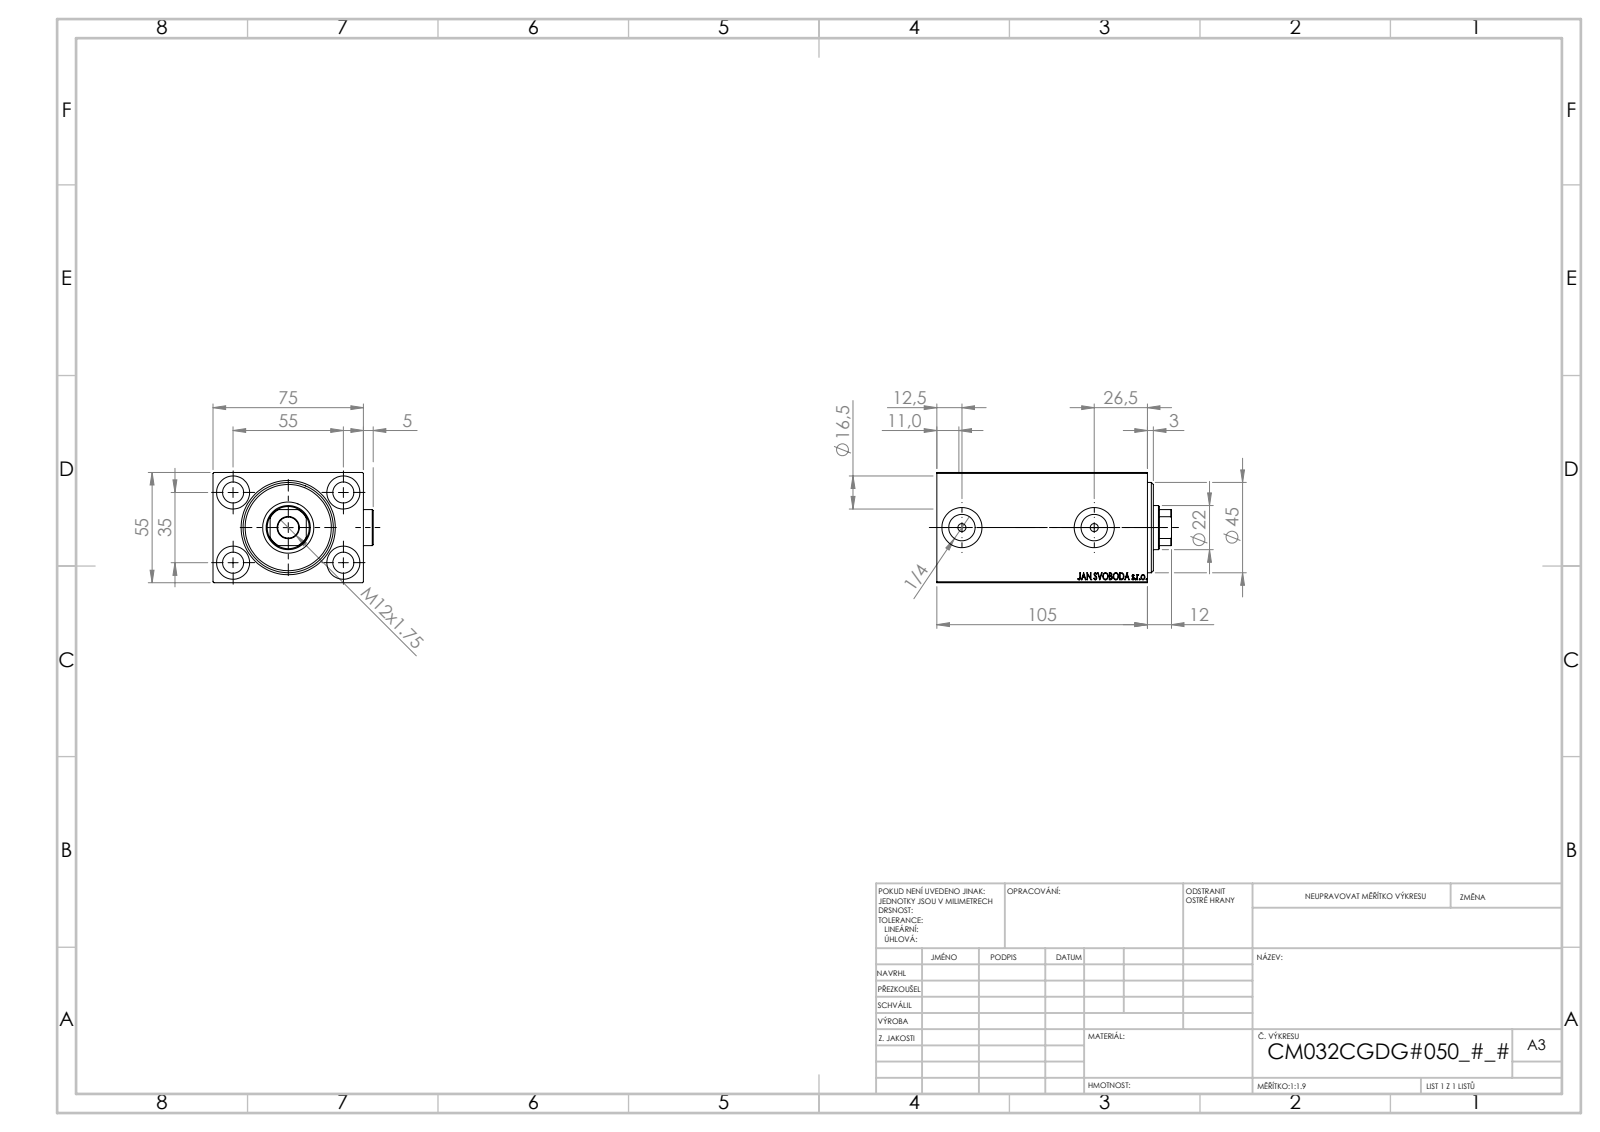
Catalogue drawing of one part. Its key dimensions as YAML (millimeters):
part_name: "V450CM_C_VCP; Zatka_OIL_PORT; V450CM_C_Body; V450CM_VC_B"
step_written_by: "SolidWorks 2019 (CONFIG_CONTROL_DESIGN)"
units: millimeters
bodies: {solids: 5, faces: 916, planar: 442, cylindrical: 76, other: 398}
overall_size: [117, 79.9, 55]
volume: 364796
surface_area: 80102
round_holes:
  - {diameter: 10.5, count: 5}
  - {diameter: 16.5, count: 4}
  - {diameter: 4, count: 2}
  - {diameter: 13.16, count: 2}
  - {diameter: 20, count: 2}
  - {diameter: 22, count: 1}
  - {diameter: 25.5, count: 1}
  - {diameter: 32, count: 1}
  - {diameter: 34, count: 1}
  - {diameter: 45, count: 1}
round_bosses_or_shafts:
  - {diameter: 18, count: 2}
partial_cylinders:
  - {radius: 10.5, count: 1}
face_to_face_distances: [55, 75, 5, 10, 95, 105, 100, 90, 74.9, 83]
hole_center_spacings: [32.6, 35, 55, 65.19, 66]
